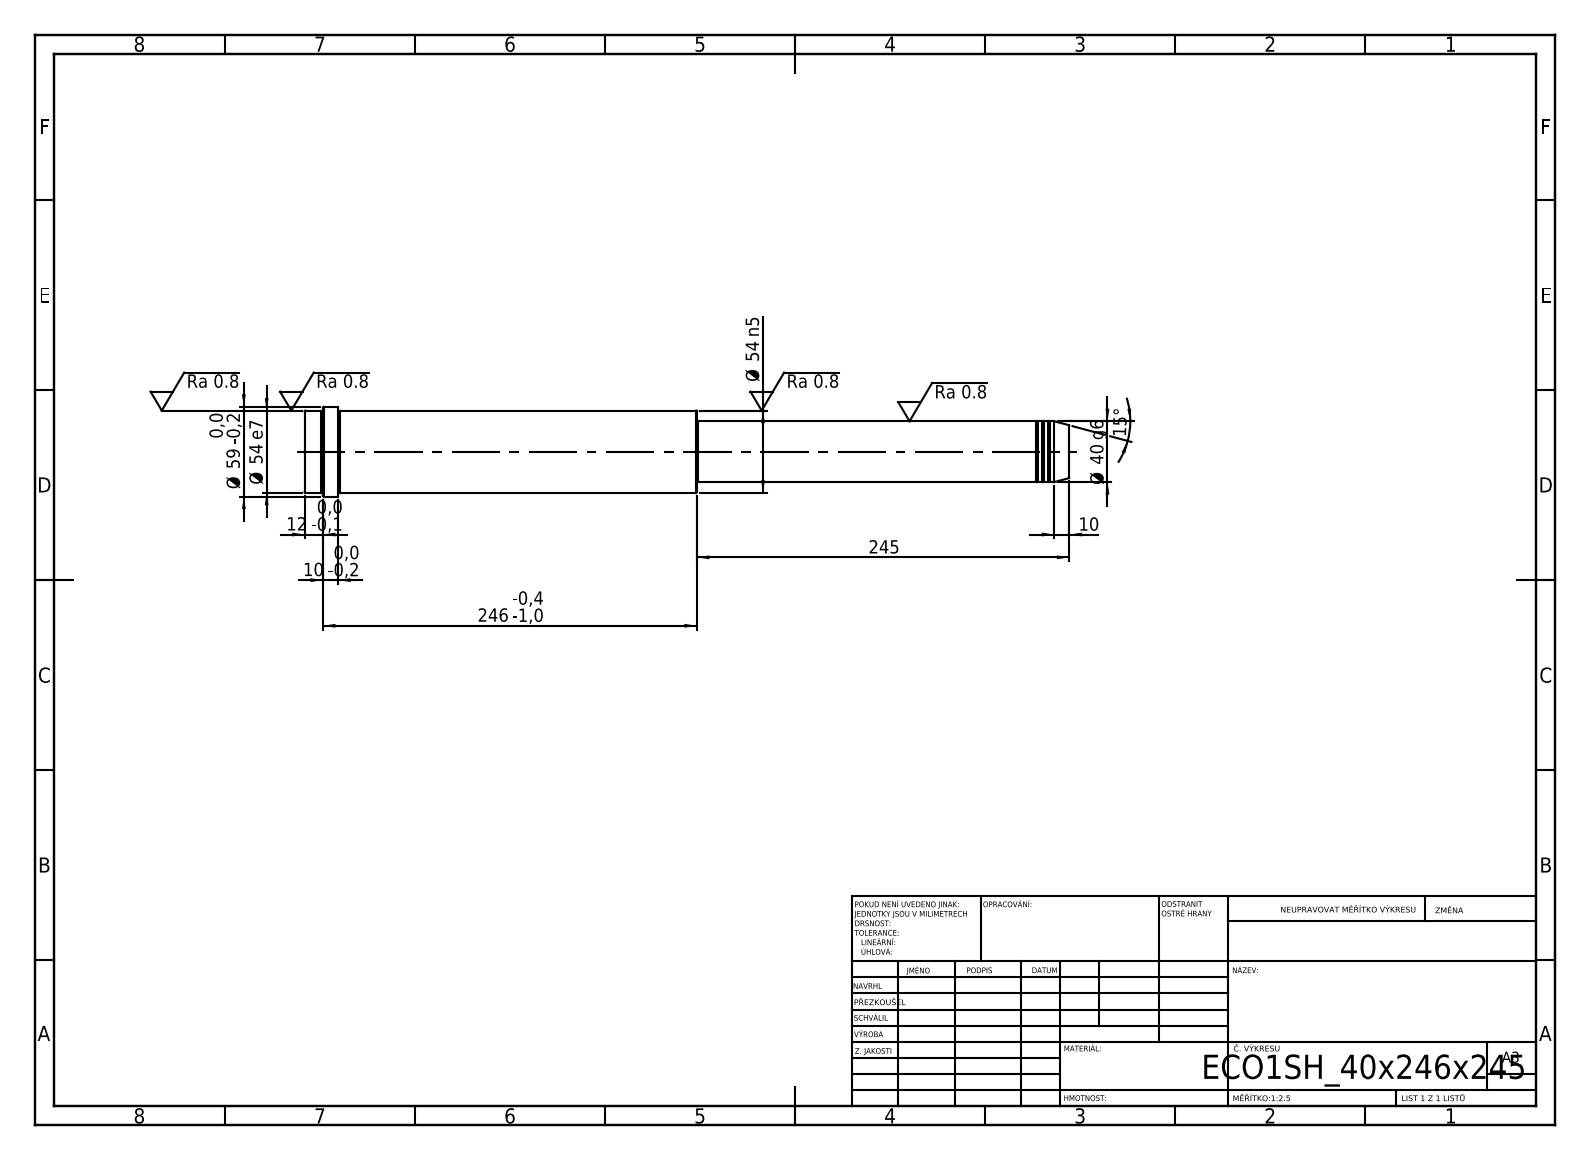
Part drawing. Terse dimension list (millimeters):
written by: SolidWorks 2019 (CONFIG_CONTROL_DESIGN)
unit: mm
bodies: 1 solid, 52 faces (6 planar, 16 cylindrical, 30 other)
size: 503 × 59 × 59
volume: 901 173 mm³; area: 80 171 mm²
bosses: 1× ⌀59, 1× ⌀54, 1× ⌀40, 1× ⌀39
face distances: 258, 245, 503, 481, 236, 22, 491, 246, 10, 12
